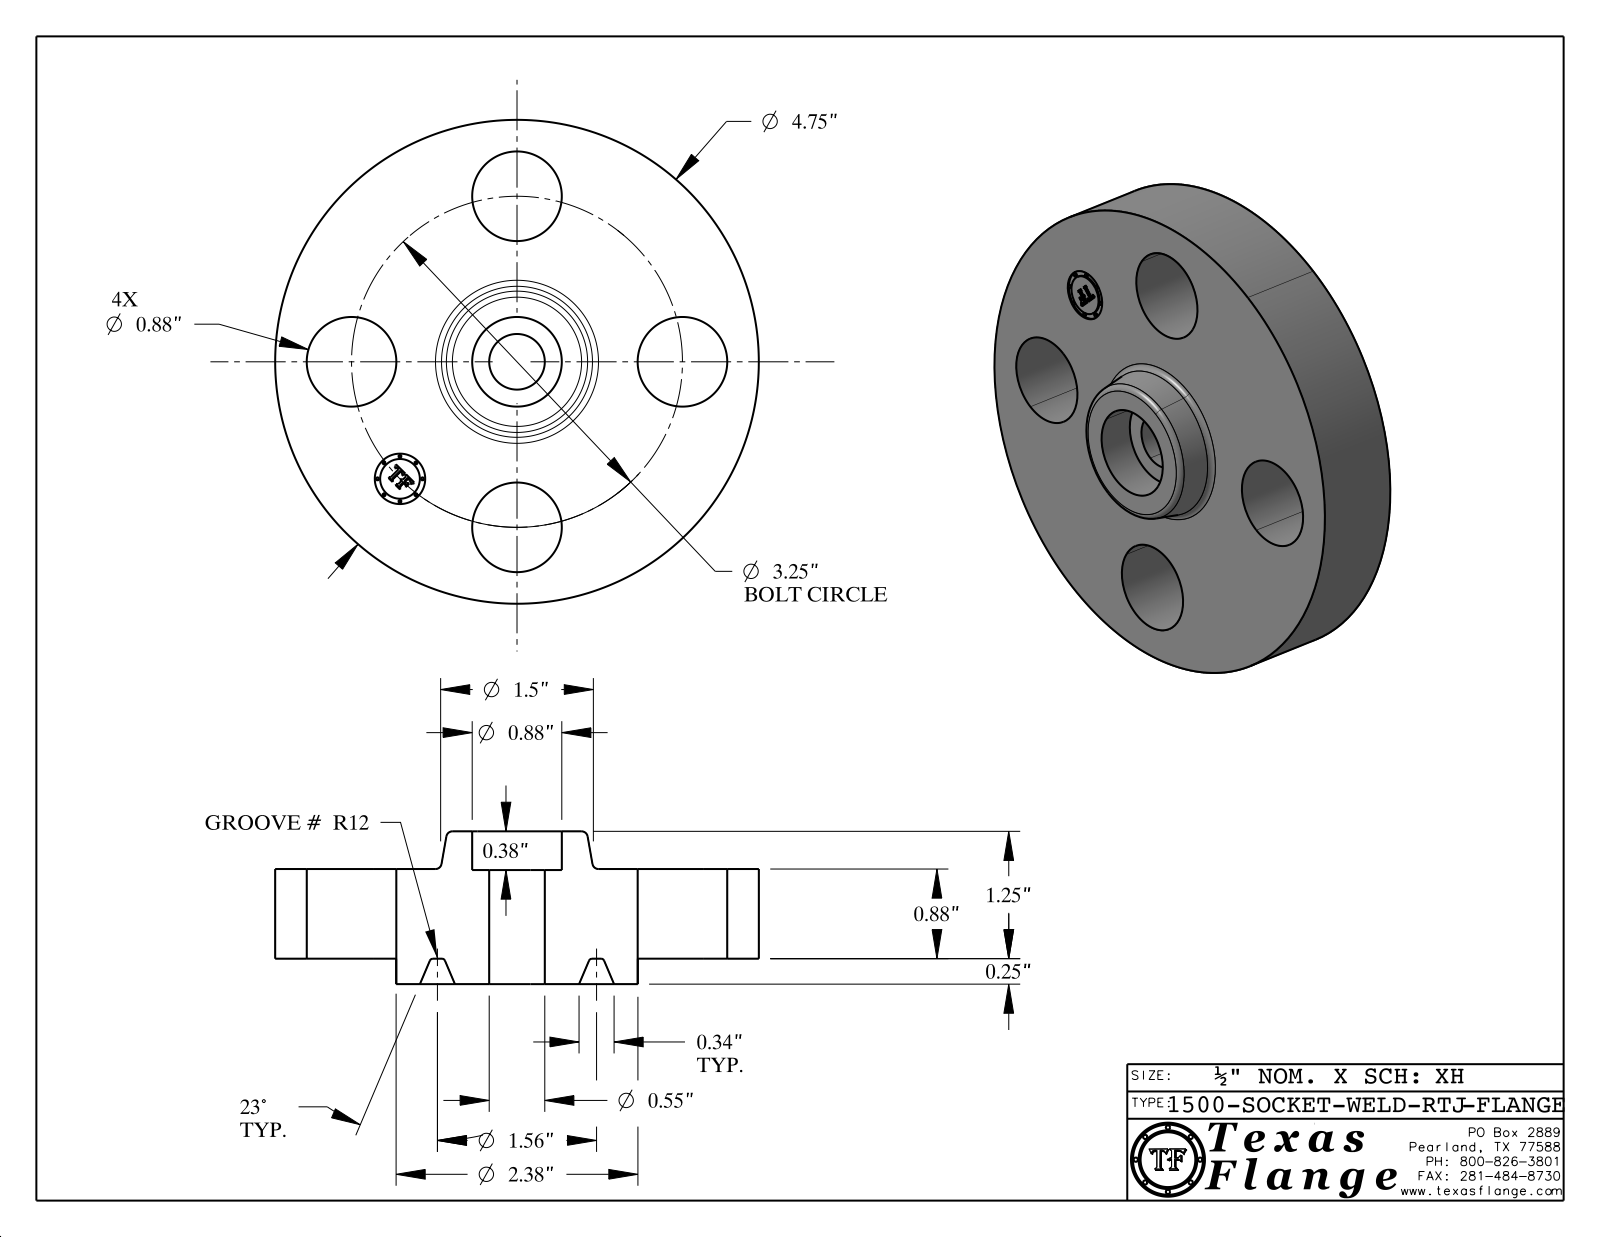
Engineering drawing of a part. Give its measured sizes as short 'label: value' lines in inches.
name: 1500-SOCKET-WELD-RTJ
written by: CATIA V5 STEP AP214 (AUTOMOTIVE_DESIGN)
unit: in
bodies: 1 solid, 426 faces (372 planar, 40 cylindrical, 14 other)
size: 4.75 × 4.75 × 1.5
volume: 14.37 in³; area: 60.73 in²
holes: 5× ⌀0.88, 1× ⌀0.495, 1× ⌀0.546
bosses: 8× ⌀0.03, 1× ⌀4.75, 1× ⌀2.375, 1× ⌀0.39
face distances: 0.88, 0.25, 1.13, 1.5, 1.25, 0.37, 1.12, 0.87, 0.38, 1.115
hole spacings: 1.625, 2.298, 1.244, 3.003, 3.25
